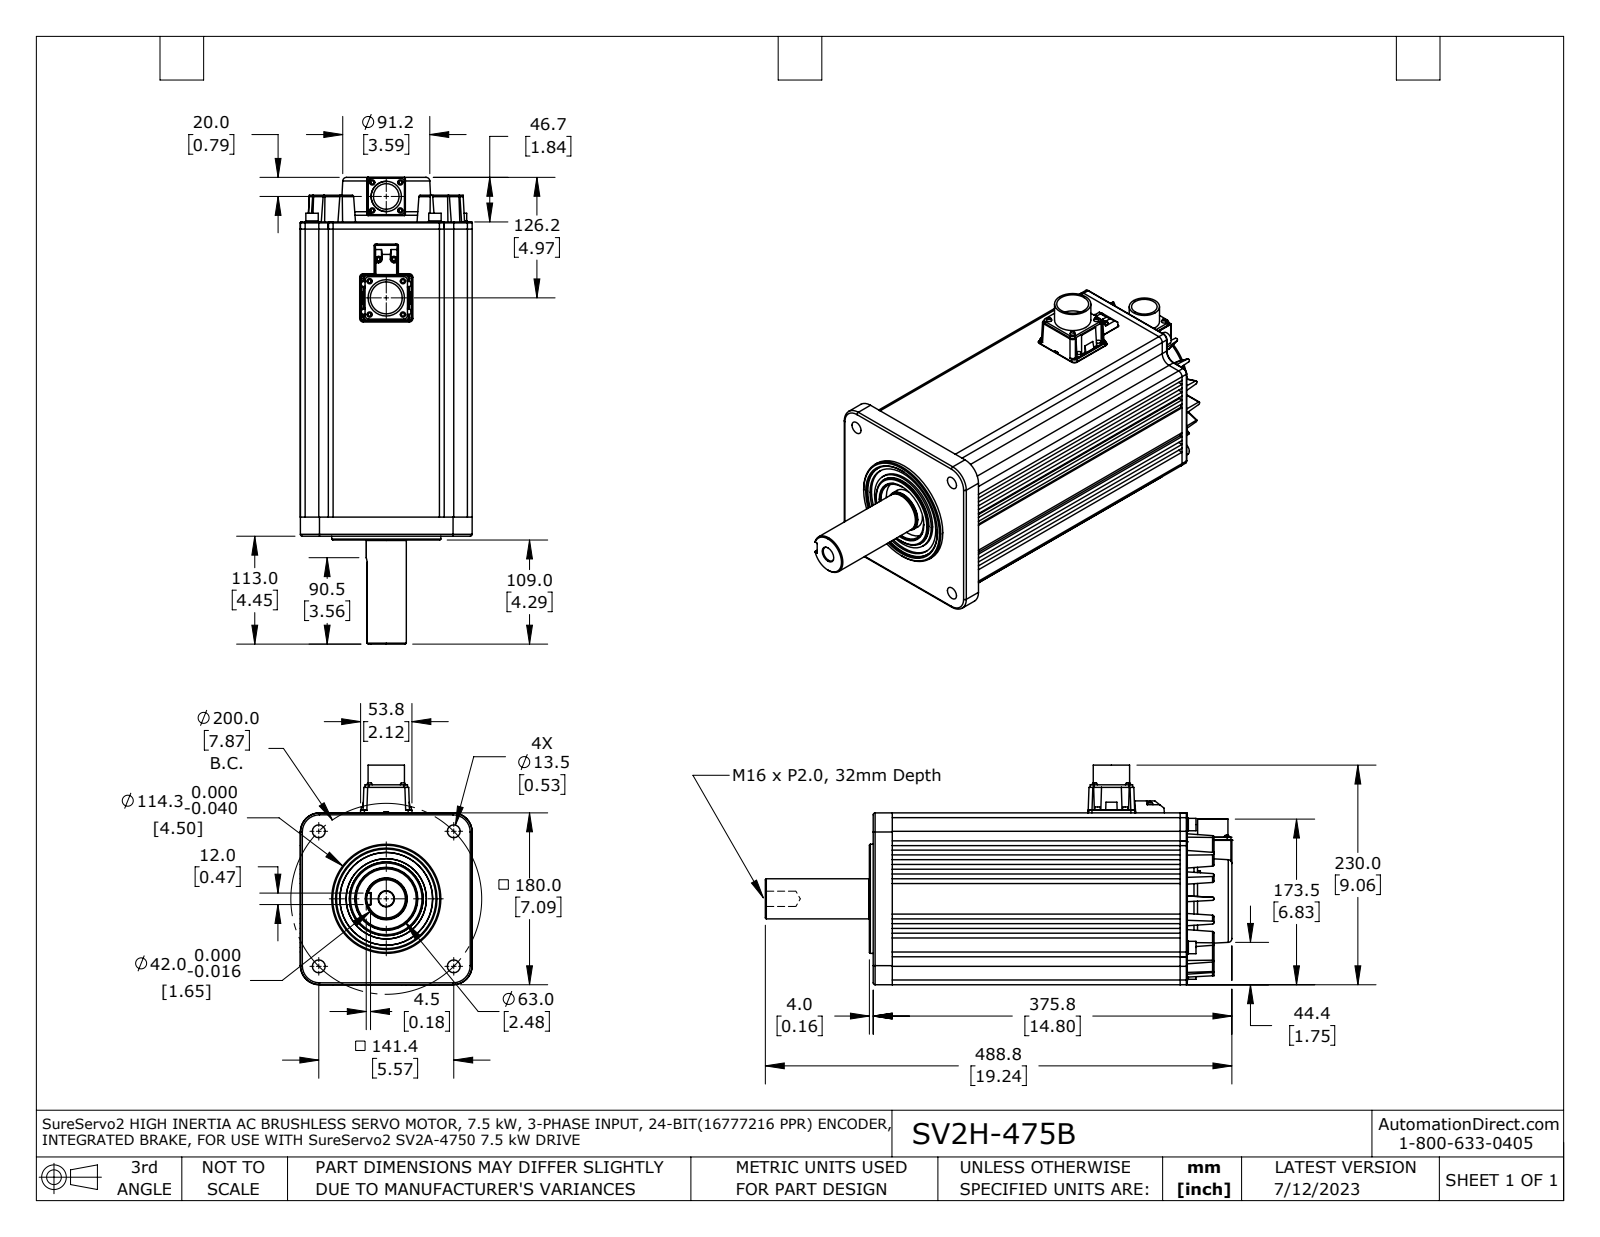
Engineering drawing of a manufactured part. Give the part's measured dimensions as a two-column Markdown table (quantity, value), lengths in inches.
| quantity | value |
| --- | --- |
| part name | SV2H-475B |
| STEP written by | SolidWorks 2021 (AUTOMOTIVE_DESIGN) |
| units | inches |
| bodies | 1 solid, 617 faces (328 planar, 190 cylindrical, 99 other) |
| overall size | 19.244 × 9.056 × 7.087 |
| volume | 614.1 in³ |
| surface area | 707.3 in² |
| round holes (diameter × count) | 0.531 × 4, 0.315 × 2, 0.63 × 1, 1.058 × 1, 1.317 × 1, 2.48 × 1 |
| round bosses / shafts (diameter × count) | 0.217 × 7, 0.528 × 4, 0.512 × 4, 0.236 × 2, 4.567 × 1, 4.5 × 1, 1.732 × 1, 1.673 × 1 |
| partial cylindrical surfaces (radius × count) | 0.064 × 16, 0.157 × 16, 0.197 × 16, 0.039 × 12, 0.02 × 8, 0.079 × 6, 0.15 × 4, 0.394 × 4 |
| main face-to-face distances | 0.197, 7.087, 0.394, 1.154, 0.591, 5.933, 3.031, 3.228, 2.835, 0.787 |
| hole center spacings | 3.937, 5.568, 0.824, 3.661, 4.8, 5.897, 7.559, 7.874 |
